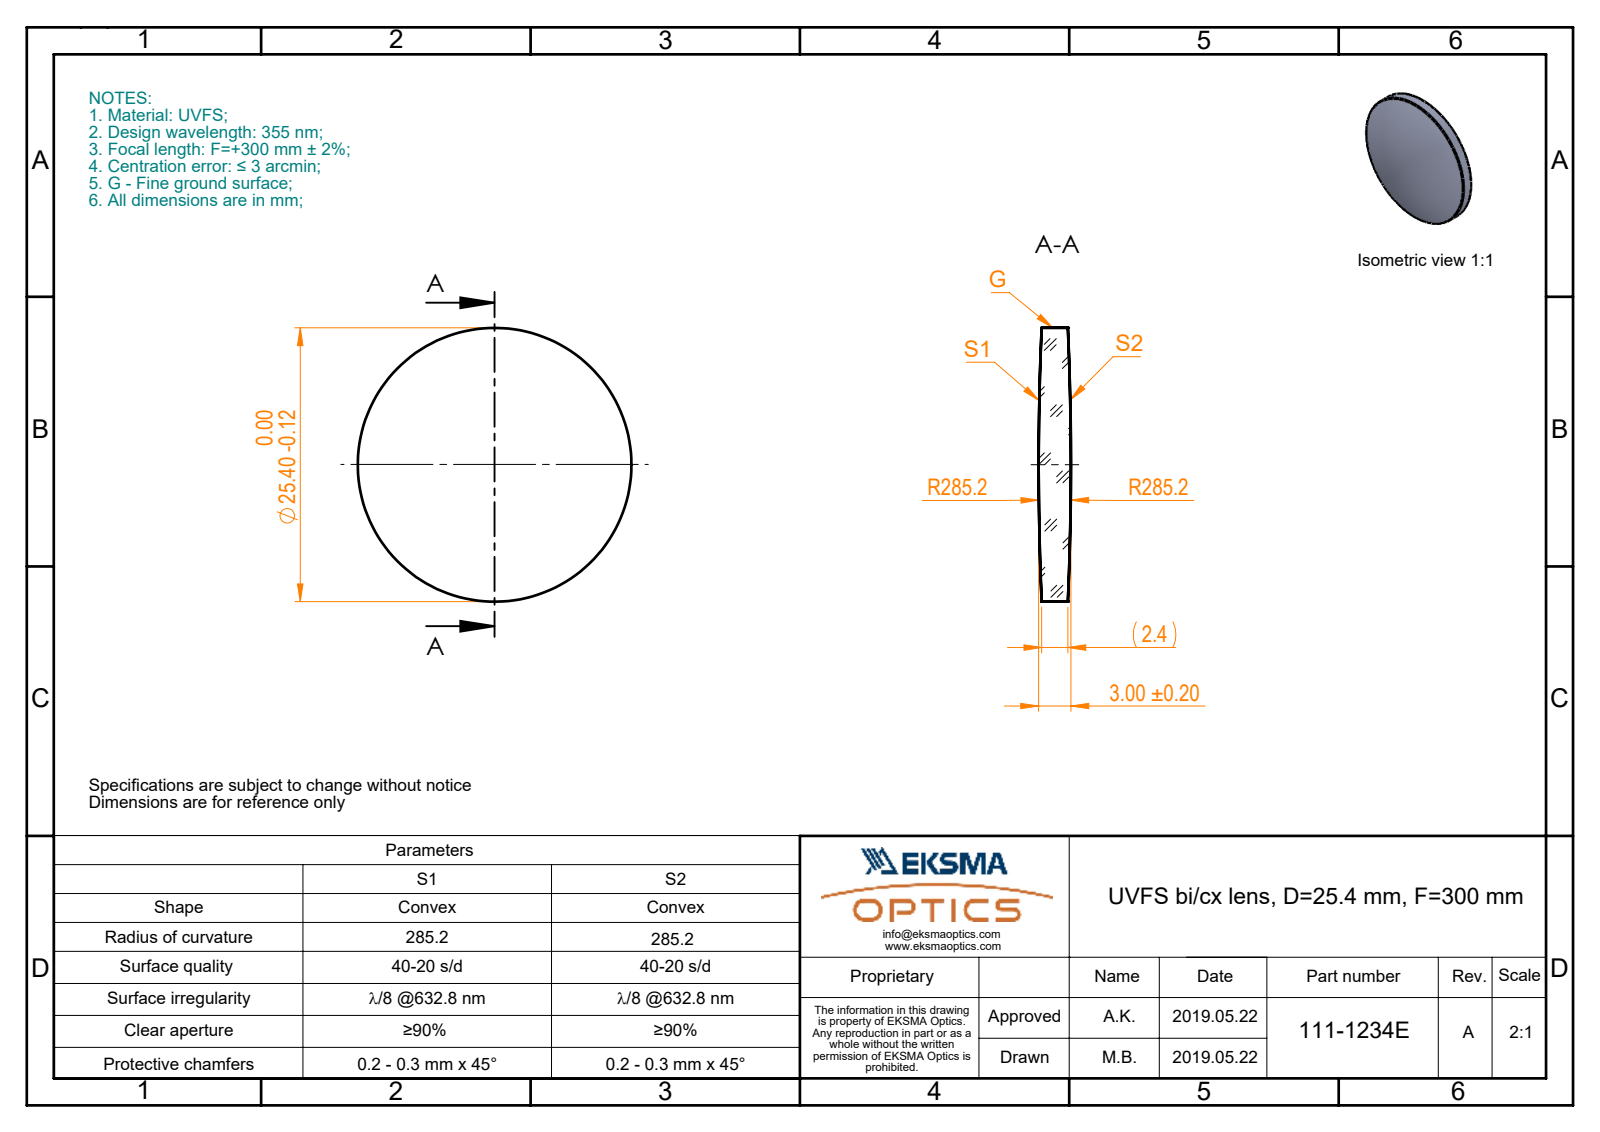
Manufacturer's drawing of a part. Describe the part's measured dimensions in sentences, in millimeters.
The part is named "111-1234E UVFS bi-cx 25.4 F300". Its 3-D file was written by "SolidWorks 2017 (CONFIG_CONTROL_DESIGN)". It is 1 solid with 6 faces: 0 planar, 2 cylindrical and 4 other. Overall it measures 25.4 by 25.4 by 3 millimeters. Its volume is 1 377 cubic millimeters and its surface area 1 208 square millimeters. Round bosses or shafts: 1 of diameter 25.4.
